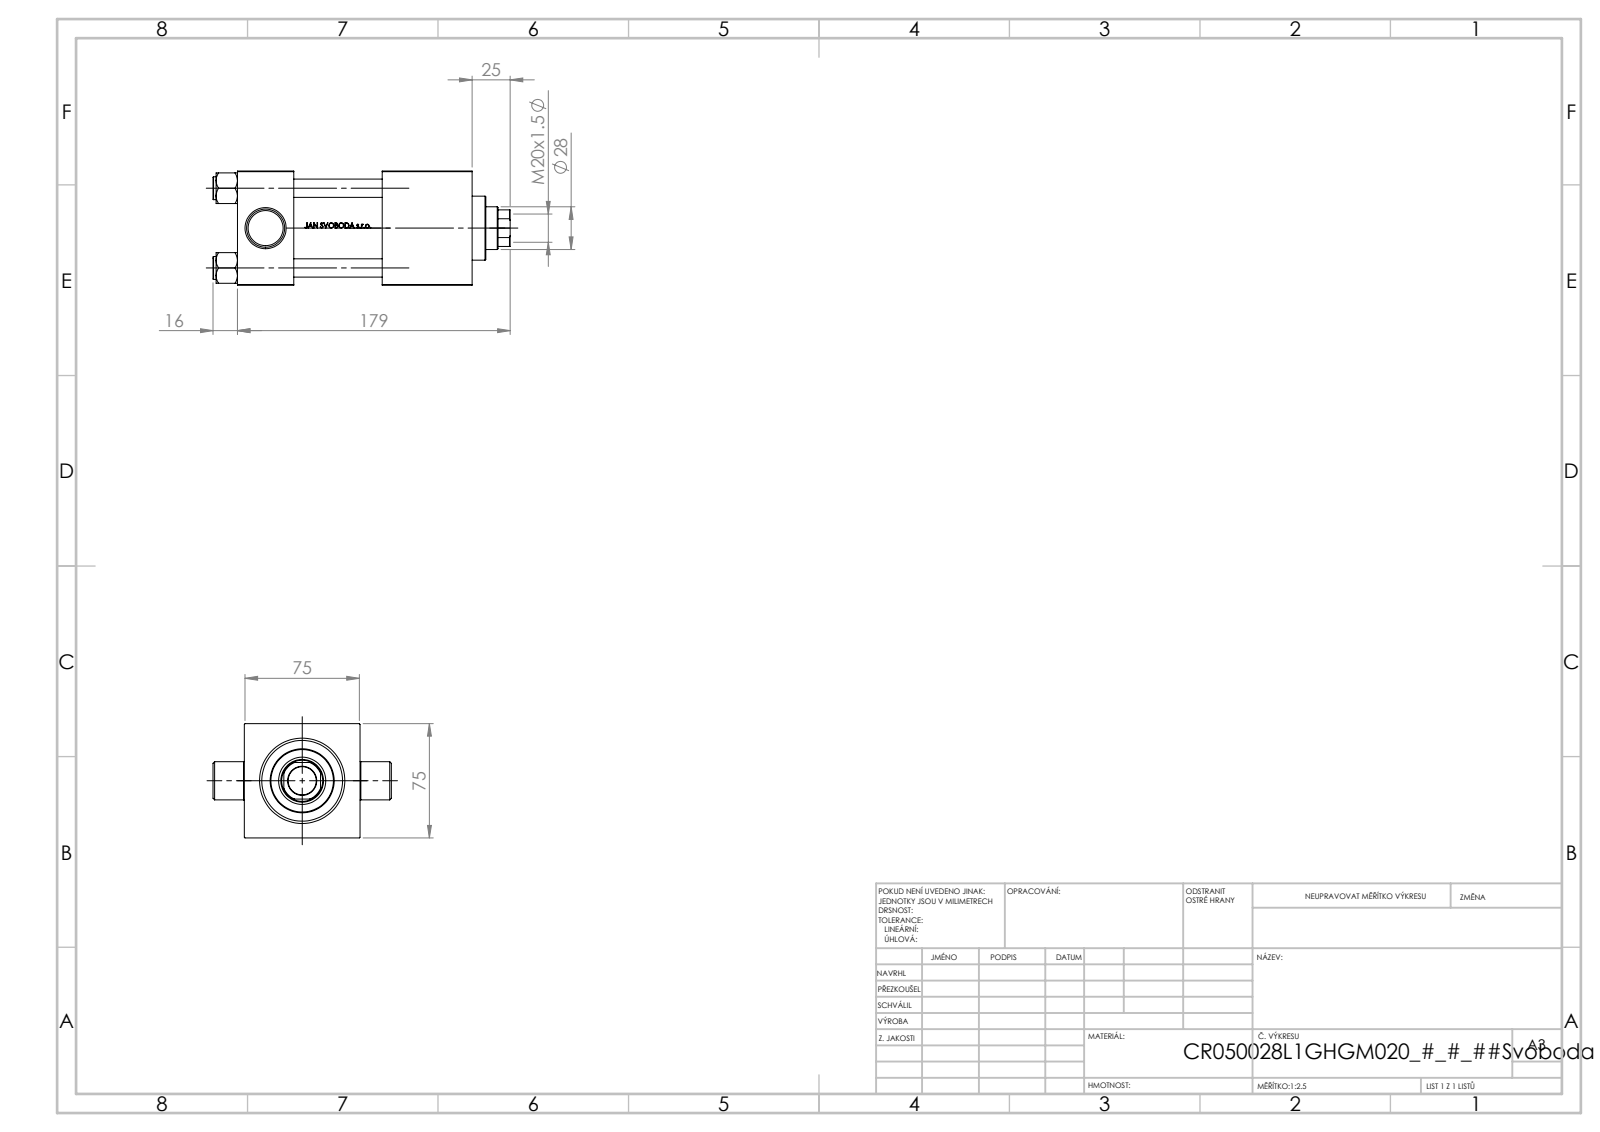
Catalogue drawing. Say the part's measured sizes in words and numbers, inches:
The part is named "V215CR_L_TYCINKA; V215CR_L_Body; V215CR_VCP_L; NUT_M5_L (+1 more)". Its 3-D file was written by "SolidWorks 2019 (CONFIG_CONTROL_DESIGN)". It is 11 solids with 1057 faces: 425 planar, 110 cylindrical and 522 other. Overall it measures 7.677 by 4.606 by 2.953 inches. Its volume is 43.53 cubic inches and its surface area 228.7 square inches. Round holes: 4 of diameter 0.472, 1 of diameter 0.276, 1 of diameter 0.728, 1 of diameter 1.102, 1 of diameter 1.22, 1 of diameter 1.614, 1 of diameter 1.969, 1 of diameter 2.087. Round bosses or shafts: 4 of diameter 0.591, 1 of diameter 2.205, 1 of diameter 1.654, 1 of diameter 0.984. Partial cylindrical surfaces (rounded edges, fillets, slot ends): 1 of radius 0.531. The main face-to-face distances are 2.953, 1.457, 4.606, 0.02, 2.992, 2.972, 6.063, 2.283, 2.323, 3.74. The hole center spacings are 1.456, 2.059, 2.912.
